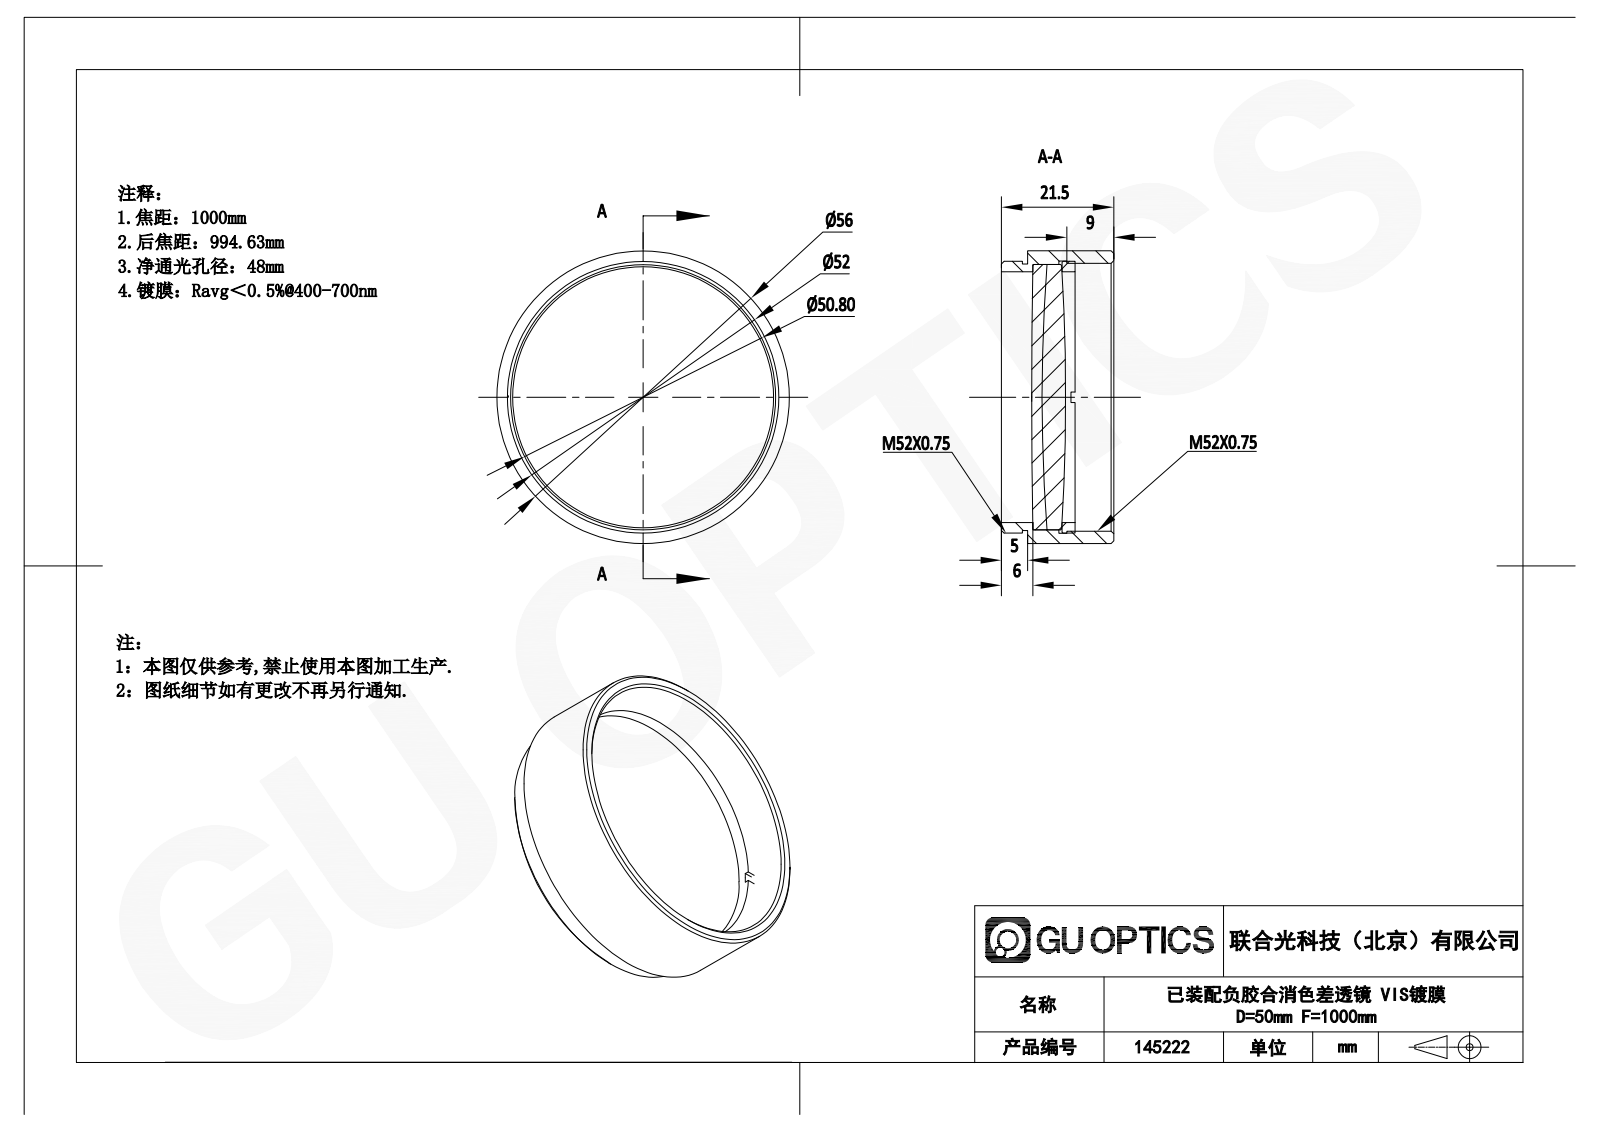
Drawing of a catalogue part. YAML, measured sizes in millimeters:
part_name: "GL31-050B-1000-VIS_Solidworks; APD-ML50-1000-VIS; M52x0.75ѹȦ"
step_written_by: "SolidWorks 2022 (AUTOMOTIVE_DESIGN)"
units: millimeters
bodies: {solids: 4, faces: 58, planar: 16, cylindrical: 22, other: 20}
overall_size: [56, 56, 21.5]
volume: 20463
surface_area: 18875
round_holes:
  - {diameter: 48, count: 1}
  - {diameter: 51.25, count: 1}
  - {diameter: 52.1, count: 1}
round_bosses_or_shafts:
  - {diameter: 56, count: 1}
  - {diameter: 52, count: 1}
  - {diameter: 51, count: 1}
  - {diameter: 50.8, count: 1}
face_to_face_distances: [7.75, 5, 6, 8.75, 1, 6.25, 2.5, 11.25, 13.75, 21.5]
